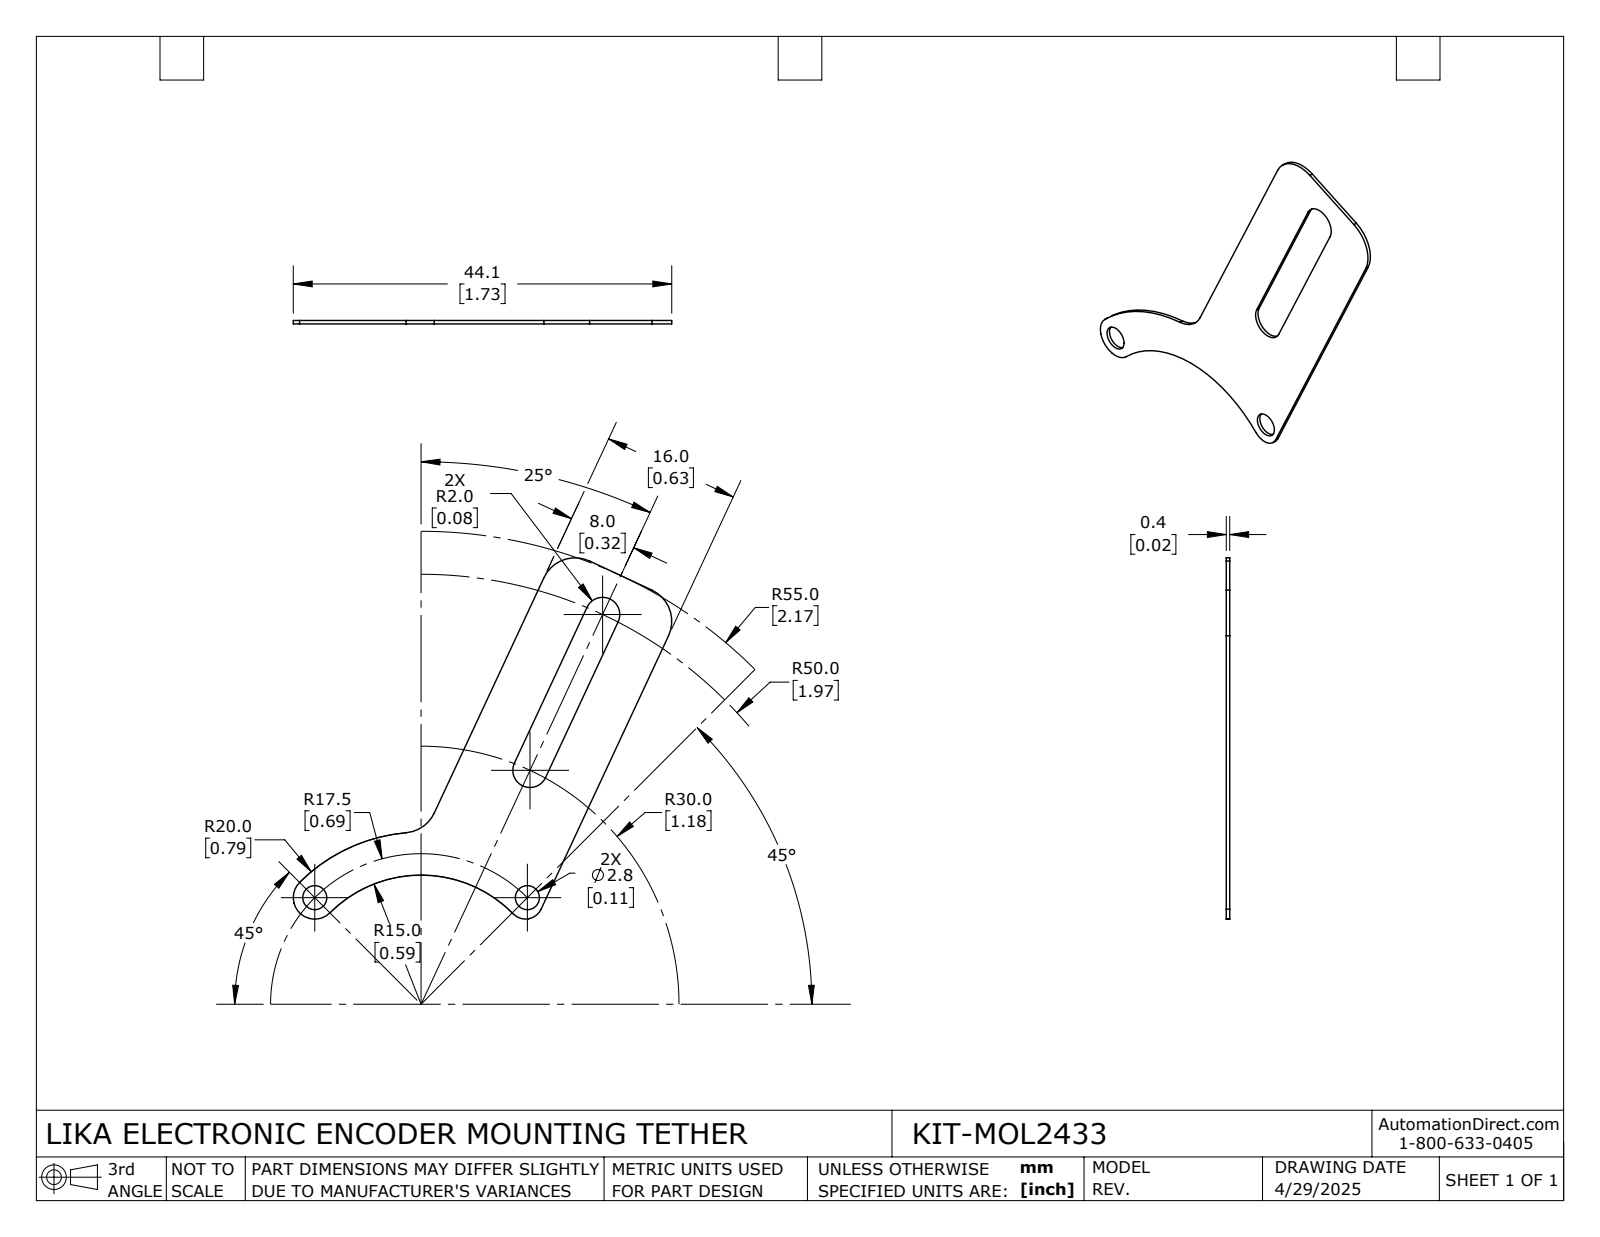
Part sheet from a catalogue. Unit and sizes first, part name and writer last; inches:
Units: inches
Overall size (bounding box): 1.735 × 1.655 × 1.299
Round holes (diameter × count): ⌀0.11 ×2
Round bosses / shafts (diameter × count): ⌀0.197 ×1, ⌀0.157 ×1
Partial cylindrical surfaces — rounded edges, fillets, slot ends (radius × count): R0.079 ×2
Main face-to-face distances: 0.016, 0.236, 0.394, 0.559, 0.543, 0.74, 0.756, 1.299, 0.63, 0.157
Hole centre spacings: 0.975
Volume: 0.046 in³ · Surface area: 2.794 in²
Bodies: 2 solids, 36 faces (10 planar, 11 cylindrical, 15 other)
Part name (STEP PRODUCT): KIT-MOL2433
STEP written by: SolidWorks 2024 (AUTOMOTIVE_DESIGN)
